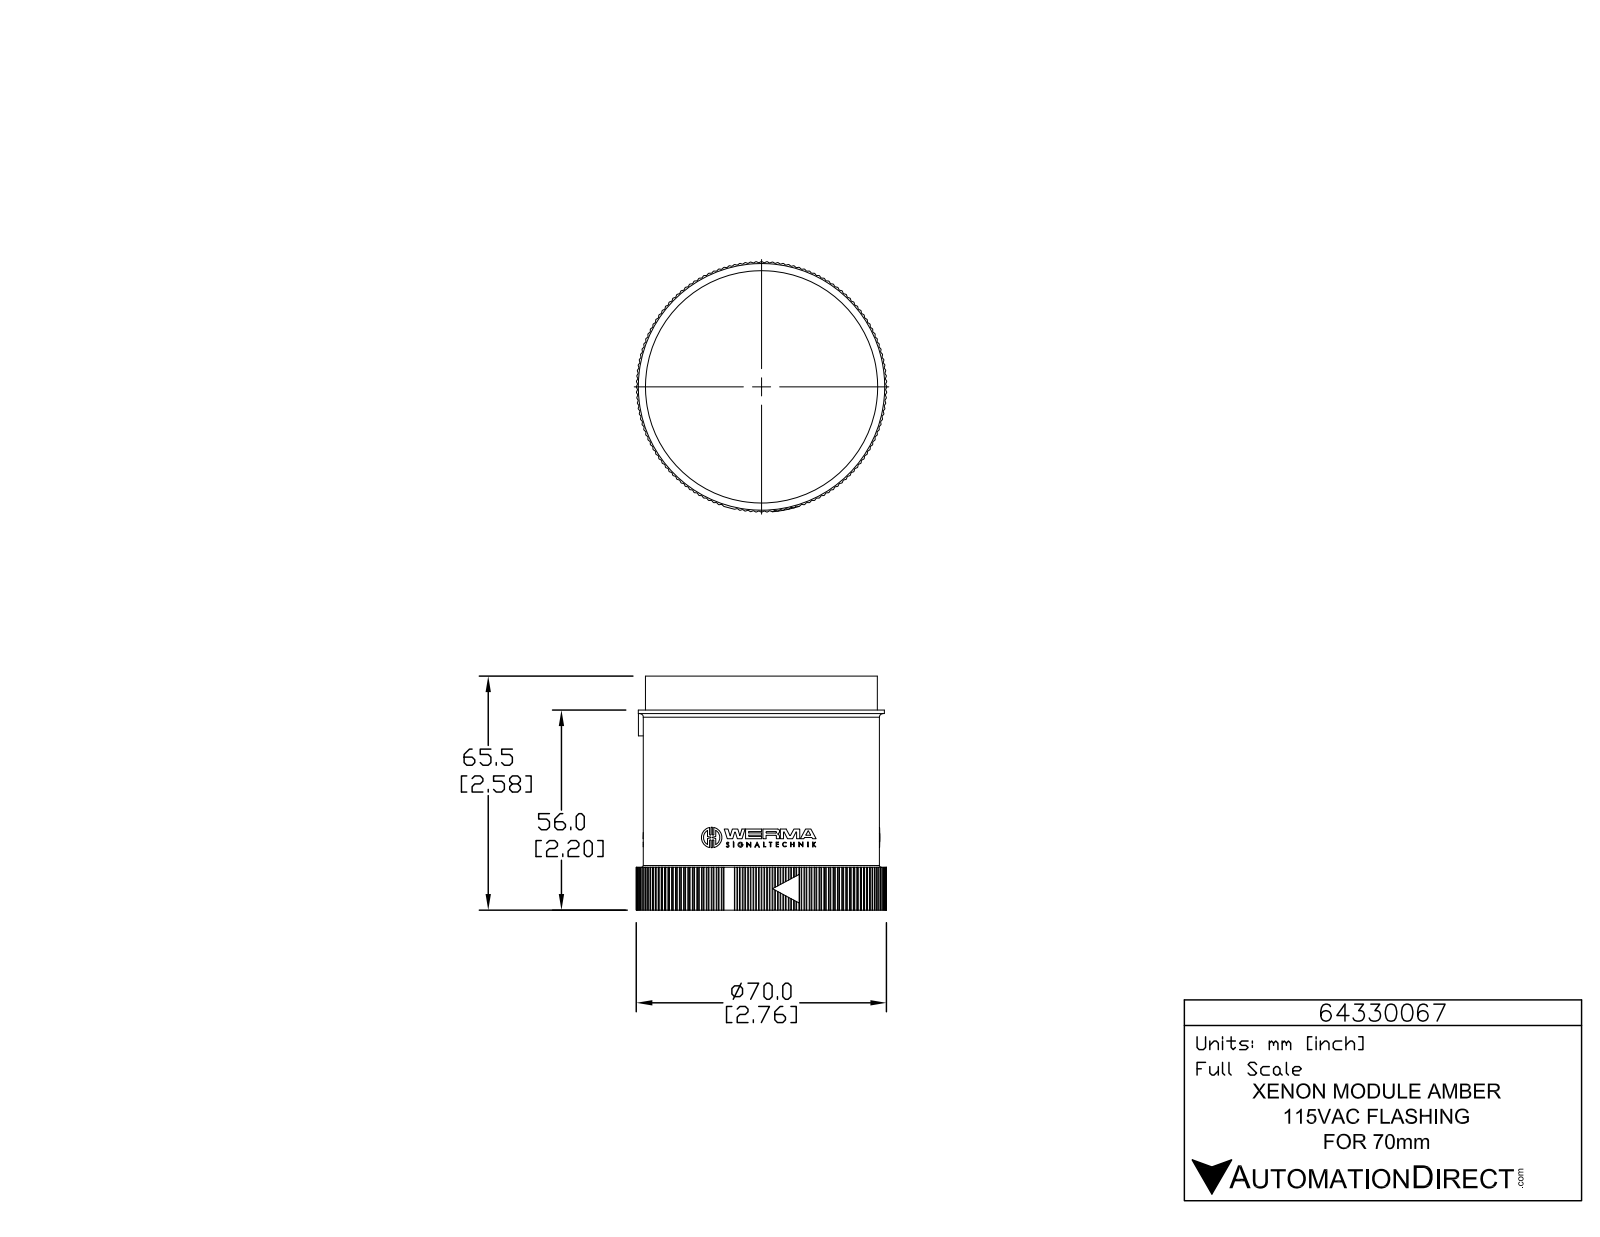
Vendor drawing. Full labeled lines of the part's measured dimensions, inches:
Part name (STEP PRODUCT): 64330067
STEP written by: SolidWorks 2015 (AUTOMOTIVE_DESIGN)
Units: inches
Bodies: 1 solid, 1400 faces (832 planar, 563 cylindrical, 5 other)
Overall size (bounding box): 2.762 × 2.762 × 2.579
Volume: 12.02 in³ · Surface area: 37.48 in²
Round holes (diameter × count): ⌀0.039 ×3, ⌀2.575 ×1
Round bosses / shafts (diameter × count): ⌀0.226 ×3, ⌀0.056 ×3, ⌀2.717 ×1, ⌀2.606 ×1, ⌀2.559 ×1
Partial cylindrical surfaces — rounded edges, fillets, slot ends (radius × count): R0.008 ×285, R0.008 ×6, R0.008 ×6, R0.008 ×6, R0.131 ×6, R0.004 ×3, R0.005 ×3, R0.008 ×3
Main face-to-face distances: 2.201, 2.451, 0.378, 2.579, 2.205, 1.827, 0.374, 2.452, 0.472, 0.094
